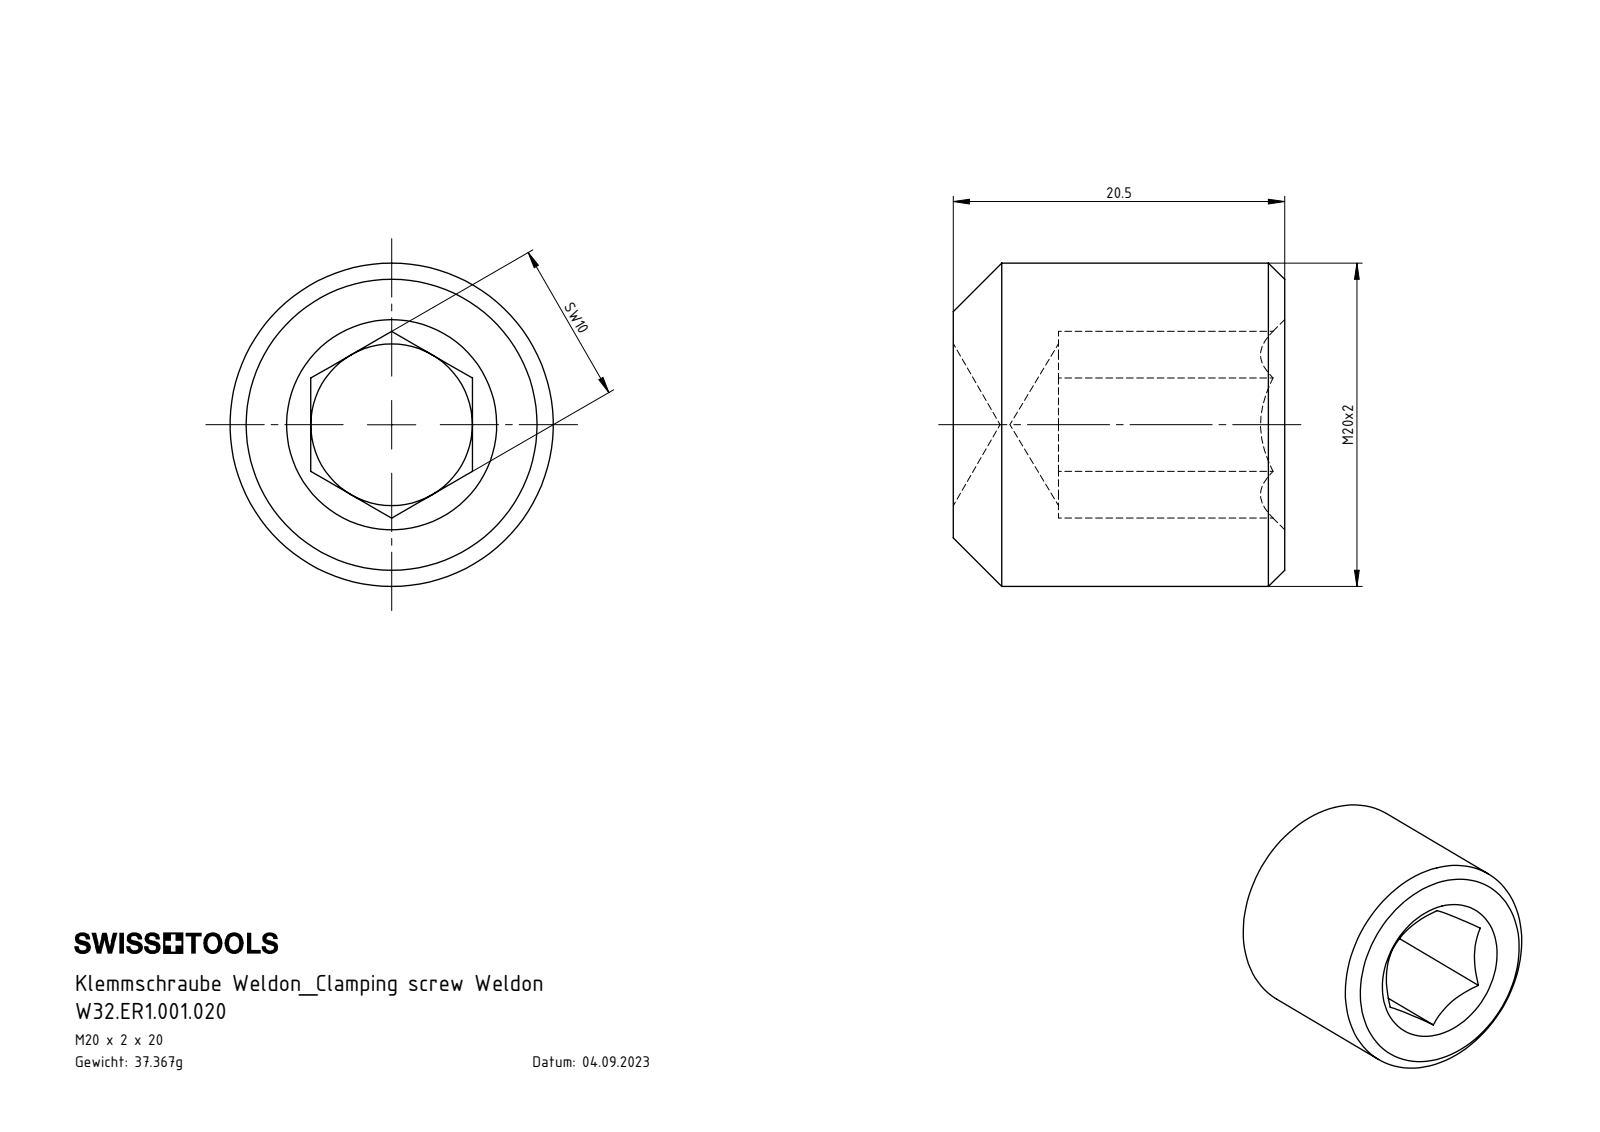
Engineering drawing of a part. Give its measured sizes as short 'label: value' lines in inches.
name: W32.ER1.001.020
written by: SolidWorks 2017 (AUTOMOTIVE_DESIGN)
unit: in
bodies: 1 solid, 26 faces (14 planar, 2 cylindrical, 10 other)
size: 0.807 × 0.787 × 0.787
volume: 0.29 in³; area: 3.477 in²
bosses: 1× ⌀0.787
face distances: 0.394, 0.807, 0.551, 0.256
